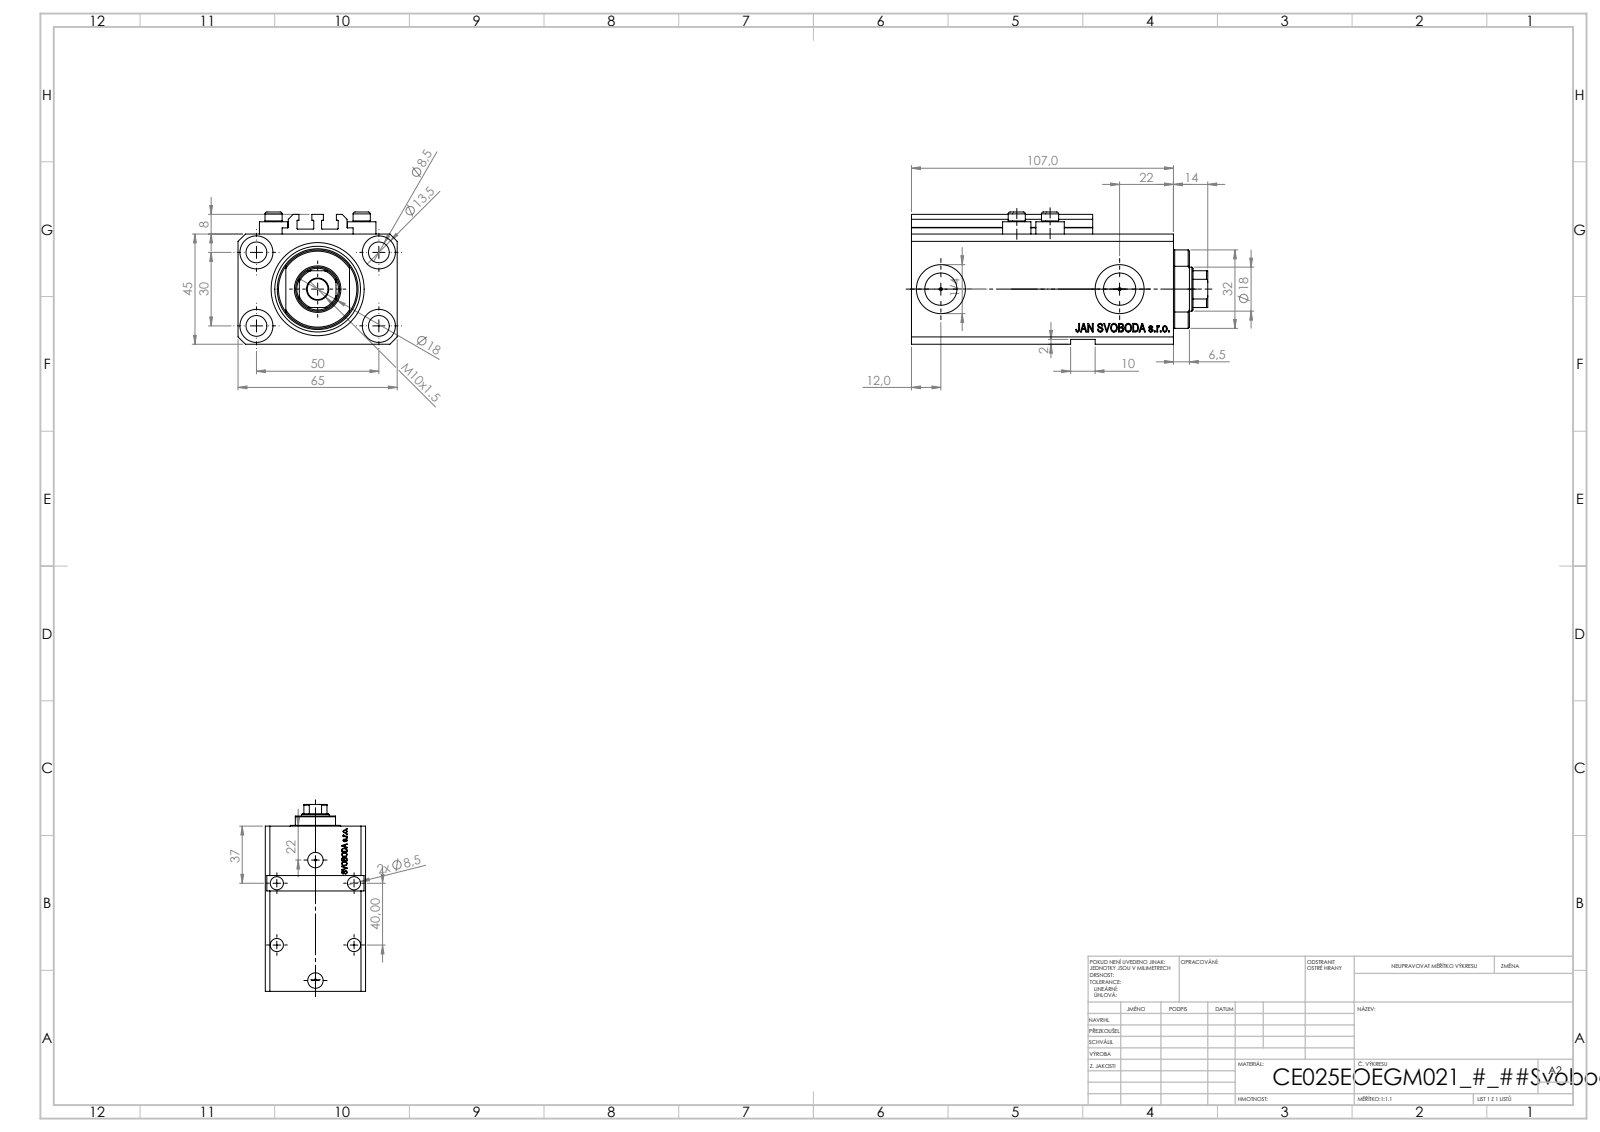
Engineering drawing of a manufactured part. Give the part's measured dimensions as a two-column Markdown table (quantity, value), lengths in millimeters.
| quantity | value |
| --- | --- |
| part name | V250CE_VC_E; ALLEN BOLT V250CE; V250CE_E_Body; V250CE_C_VCP |
| STEP written by | SolidWorks 2019 (CONFIG_CONTROL_DESIGN) |
| units | millimeters |
| bodies | 8 solids, 1087 faces (511 planar, 146 cylindrical, 430 other) |
| overall size | 121 × 65 × 54 |
| volume | 273 399 mm³ |
| surface area | 76 876 mm² |
| round holes (diameter × count) | 8.5 × 9, 1.25 × 4, 4 × 4, 13.5 × 4, 10 × 2, 13.16 × 2, 20 × 2, 18 × 1, 25 × 1, 38 × 1 |
| round bosses / shafts (diameter × count) | 11.6 × 4, 7 × 4 |
| partial cylindrical surfaces (radius × count) | 0.2 × 10, 8.5 × 1, 16 × 1 |
| main face-to-face distances | 45, 65, 93, 2, 14, 47, 107, 2.5, 10, 20.5 |
| hole center spacings | 29.15, 50, 13.6, 14.76, 15.12, 27.51, 27.89, 30 |
